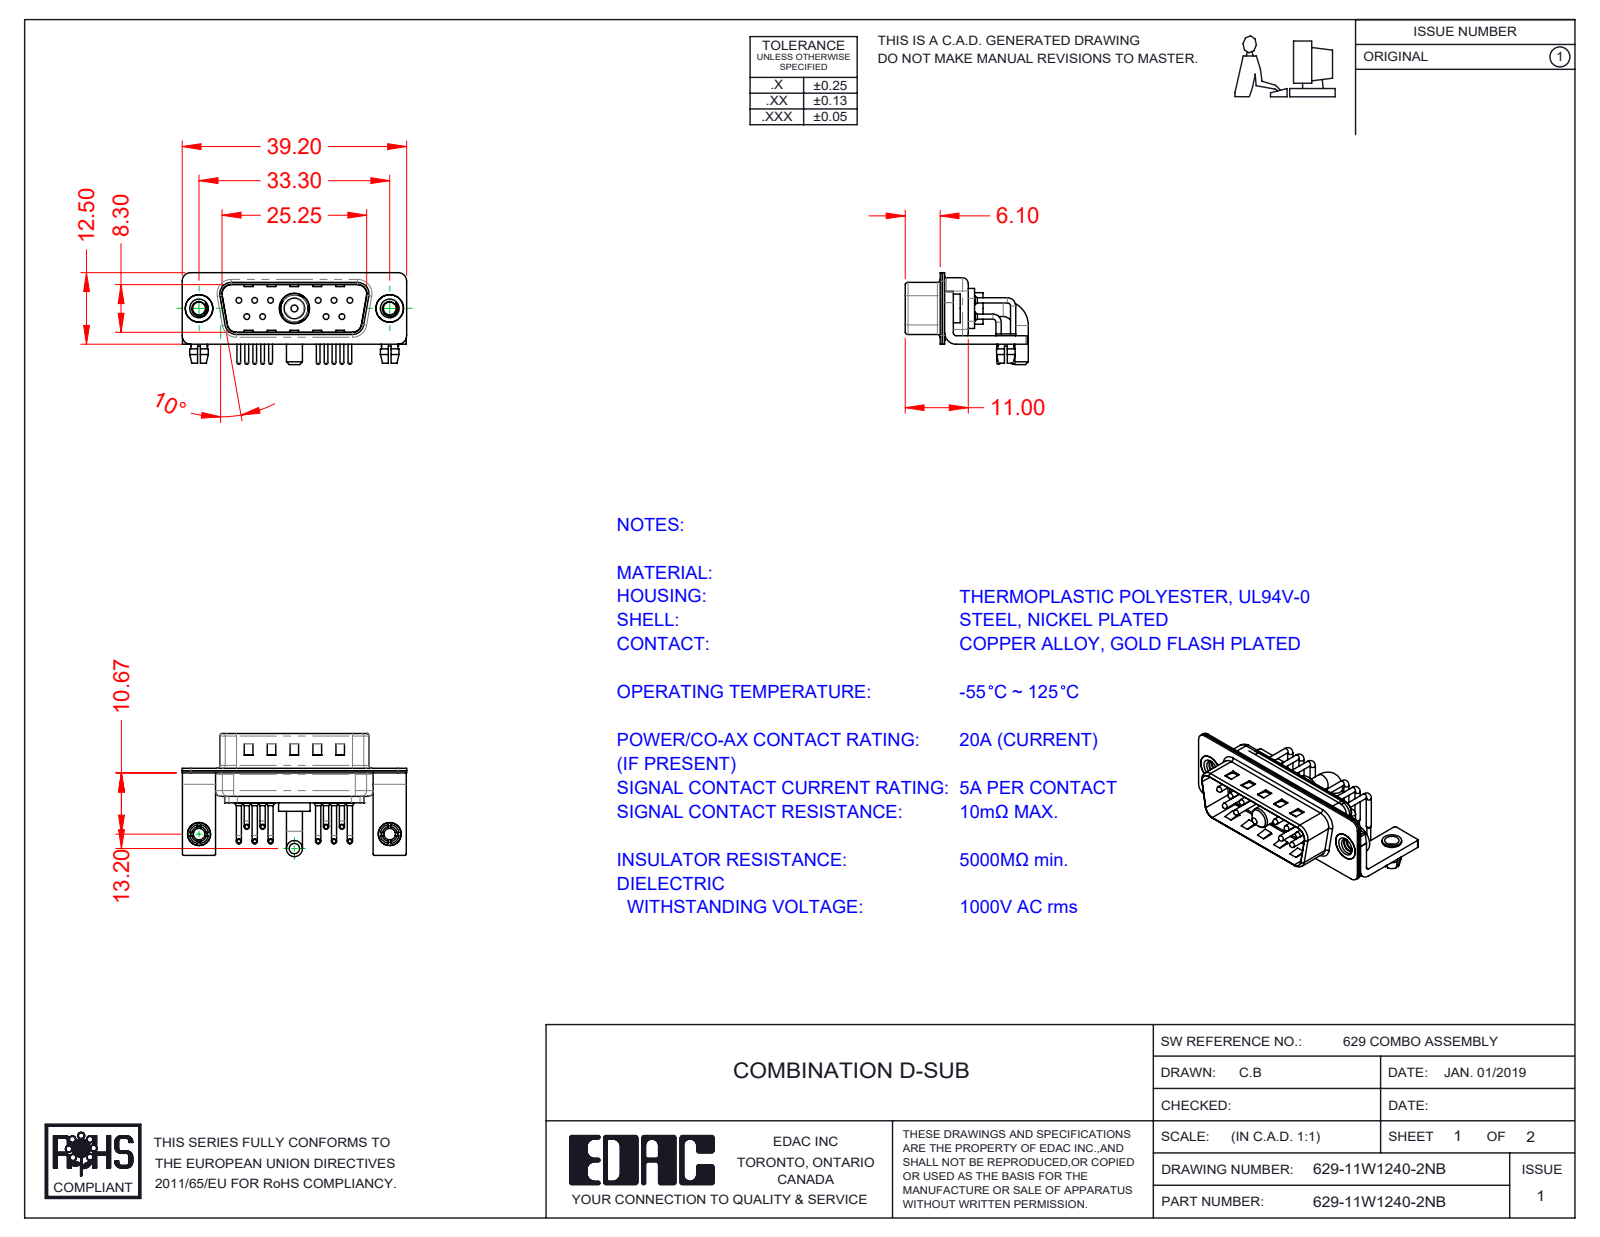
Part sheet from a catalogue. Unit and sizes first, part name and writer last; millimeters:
Units: millimetres
Overall size (bounding box): 39.2 × 21.5 × 16.05
Round holes (diameter × count): ⌀2 ×12, ⌀0.75 ×10, ⌀1.6 ×10, ⌀2.26 ×2, ⌀2.5 ×2, ⌀3.2 ×2, ⌀4 ×2, ⌀4.8 ×2, ⌀4.85 ×1, ⌀5.3 ×1
Round bosses / shafts (diameter × count): ⌀0.9 ×20, ⌀1.5 ×10, ⌀1 ×10, ⌀0.65 ×10, ⌀5 ×2, ⌀4.9 ×2, ⌀4 ×2, ⌀3.4 ×2
Partial cylindrical surfaces — rounded edges, fillets, slot ends (radius × count): R0.25 ×16, R1.5 ×16, R2 ×13, R1.01 ×10, R0.5 ×9, R1.6 ×8, R1 ×7, R0.6 ×4
Main face-to-face distances: 0.4, 0.8, 1.5, 9.5, 9.1, 0.6, 8.7, 9.9, 1.2, 0.75
Hole centre spacings: 3.16, 2.77, 13.85, 11.08, 16.62, 5.03, 5.04, 5.54
Volume: 2 411 mm³ · Surface area: 6 086 mm²
Bodies: 21 solids, 1636 faces (866 planar, 574 cylindrical, 196 other)
Part name (STEP PRODUCT): 629Combo Shell Front_15 Contacts; 629Combo Contact Row 2; 629-11W1240-2NB; 629Combo Shell Rear_15 Contacts (+6 more)
STEP written by: SolidWorks 2020 (CONFIG_CONTROL_DESIGN)
